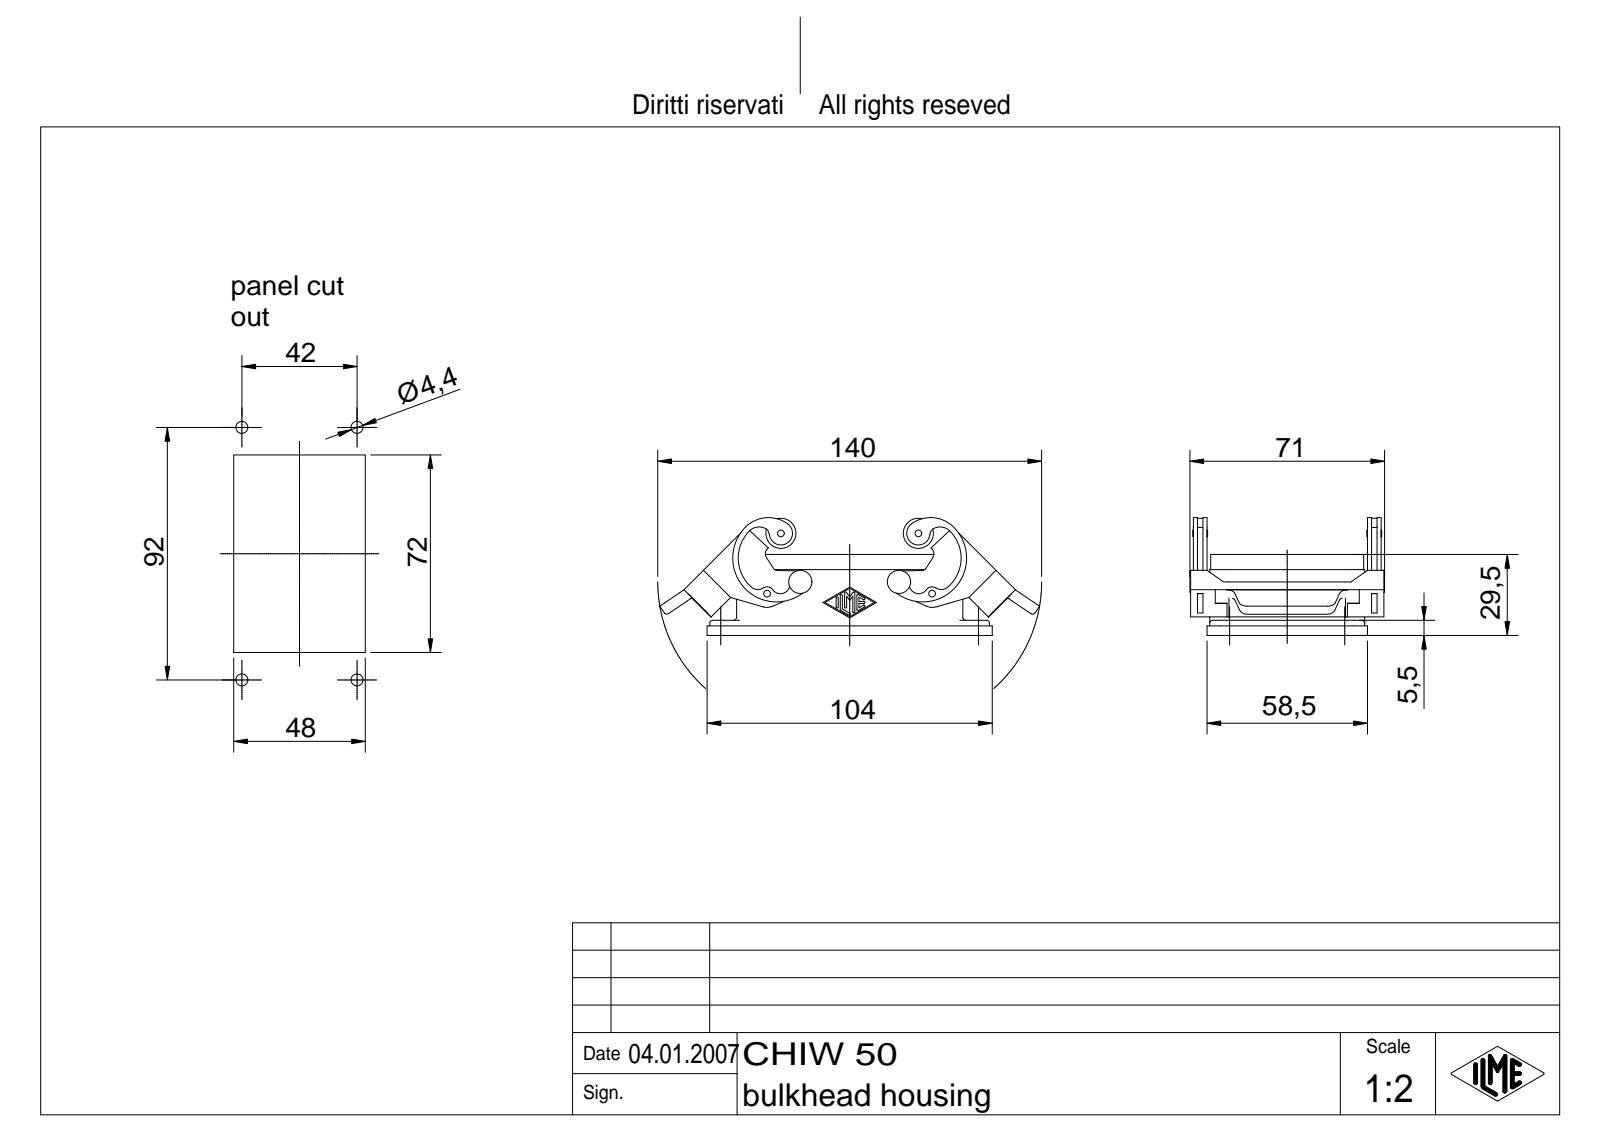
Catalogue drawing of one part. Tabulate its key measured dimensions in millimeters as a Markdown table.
| quantity | value |
| --- | --- |
| part name | CHIW 50 |
| STEP written by | Autodesk Inventor 7 (AUTOMOTIVE_DESIGN) |
| units | millimeters |
| bodies | 1 solid, 778 faces (209 planar, 238 cylindrical, 331 other) |
| overall size | 138.49 × 71 × 42.94 |
| volume | 58 568 mm³ |
| surface area | 39 922 mm² |
| round holes (diameter × count) | 2 × 4, 2.46 × 4, 3.1 × 4, 4.5 × 4, 4.6 × 4, 2.5 × 2 |
| round bosses / shafts (diameter × count) | 11 × 2, 5 × 2, 3 × 2 |
| partial cylindrical surfaces (radius × count) | 0.38 × 14, 1 × 14, 3 × 12, 2.5 × 10, 3.5 × 8, 5 × 8, 6 × 8, 1.5 × 6 |
| main face-to-face distances | 3, 4, 53.5, 5.5, 1, 3.5, 63.5, 1.35, 53.15, 2 |
| hole center spacings | 14.04, 16, 22.02, 22.56, 28.65, 42, 43.32, 59.38 |
